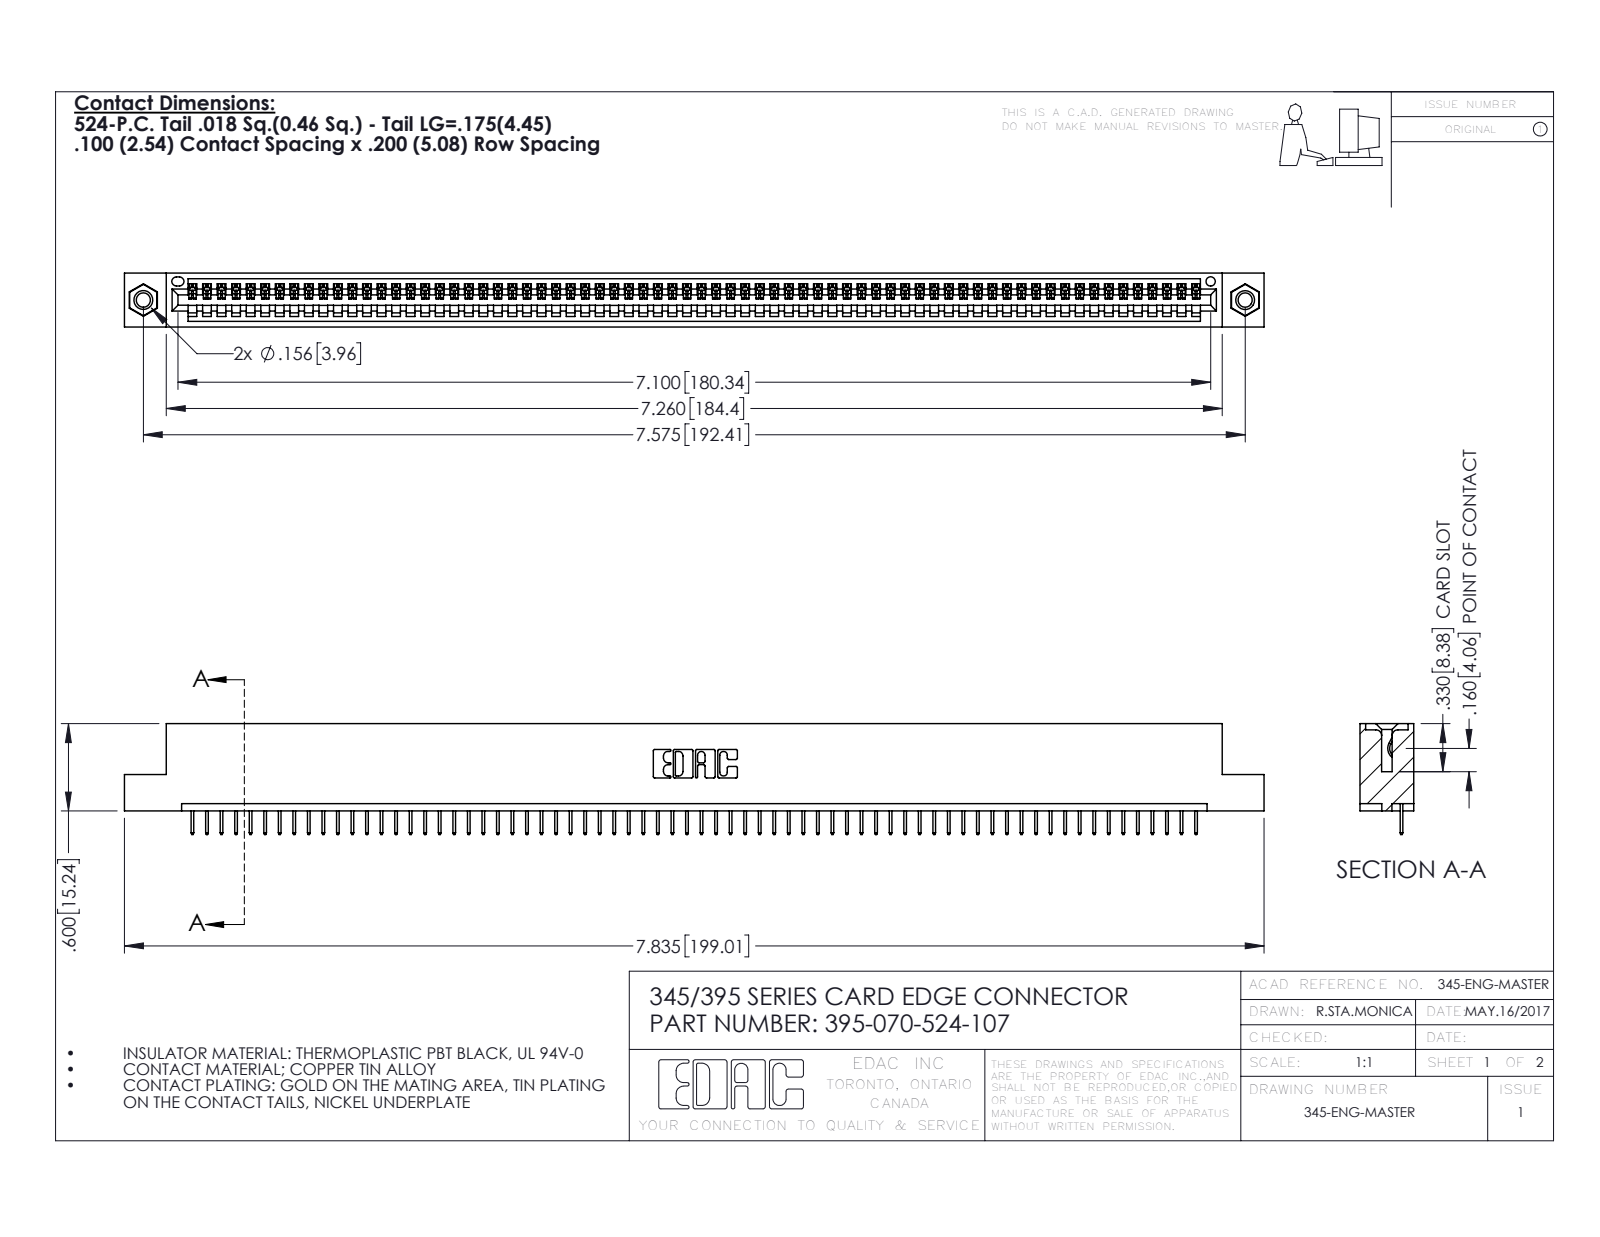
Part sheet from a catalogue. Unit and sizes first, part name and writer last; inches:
Units: inches
Overall size (bounding box): 7.835 × 0.762 × 0.37
Round holes (diameter × count): ⌀0.098 ×2, ⌀0.125 ×2, ⌀0.156 ×2, ⌀0.064 ×1
Round bosses / shafts (diameter × count): ⌀0.155 ×2
Partial cylindrical surfaces — rounded edges, fillets, slot ends (radius × count): R0.006 ×140, R0.01 ×22, R0.007 ×6, R0.031 ×6, R0.026 ×3, R0.031 ×2, R0.04 ×2, R0.014 ×1
Main face-to-face distances: 0.072, 0.298, 0.37, 0.2, 0.098, 0.272, 0.025, 0.225, 0.072, 0.149
Hole centre spacings: 0.27, 7.339, 7.575
Volume: 1.15 in³ · Surface area: 38.08 in²
Bodies: 73 solids, 4526 faces (3332 planar, 1178 cylindrical, 16 other)
Part name (STEP PRODUCT): 345 Part_Flush Mounting Lugs - 0.156 Dia-TI; 395-070-524-107; 345-250-001_345-250-005-103; 345-292-001_345-293-124
STEP written by: SolidWorks 2016 (CONFIG_CONTROL_DESIGN)
